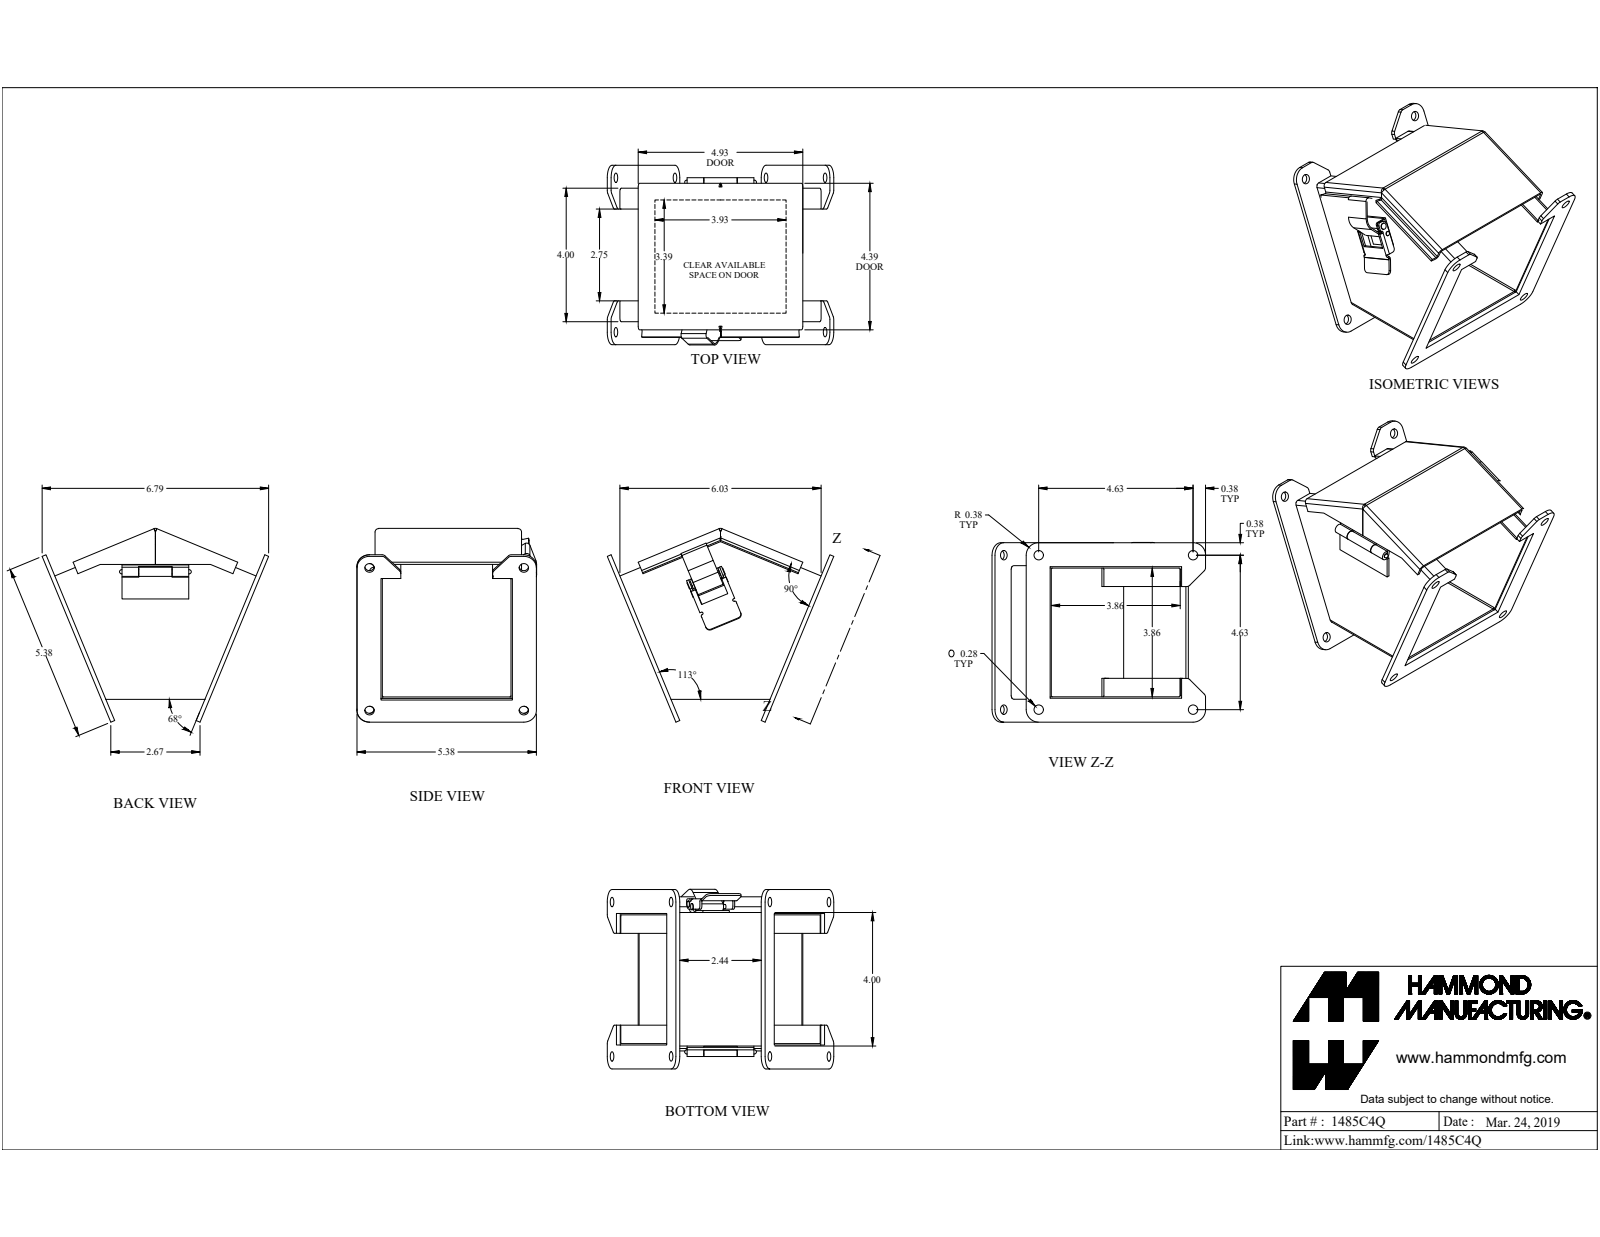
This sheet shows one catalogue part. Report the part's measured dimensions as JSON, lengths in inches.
{"part_name": "1485C4Q", "step_written_by": "SolidWorks 2019 (CONFIG_CONTROL_DESIGN)", "units": "inches", "bodies": {"solids": 10, "faces": 297, "planar": 176, "cylindrical": 109, "other": 12}, "overall_size": [6.787, 5.804, 5.383], "volume_in3": 9.517, "surface_area_in2": 250.6, "round_holes": [[0.281, 8], [0.13, 2], [0.164, 2], [0.125, 1]], "round_bosses_or_shafts": [[0.187, 3], [0.156, 2], [0.275, 1], [0.125, 1]], "partial_cylinders_radius": [[0.036, 13], [0.108, 13], [0.125, 12], [0.375, 8], [0.016, 7], [0.035, 4], [0.039, 4], [0.076, 3]], "face_to_face_distances": [0.072, 3.928, 0.125, 4, 3.856, 0.171, 0.174, 0.075, 4.075, 4.003], "hole_center_spacings": [4.625, 6.541, 0.285, 4.78, 0.284, 0.285, 1.373, 1.373]}
